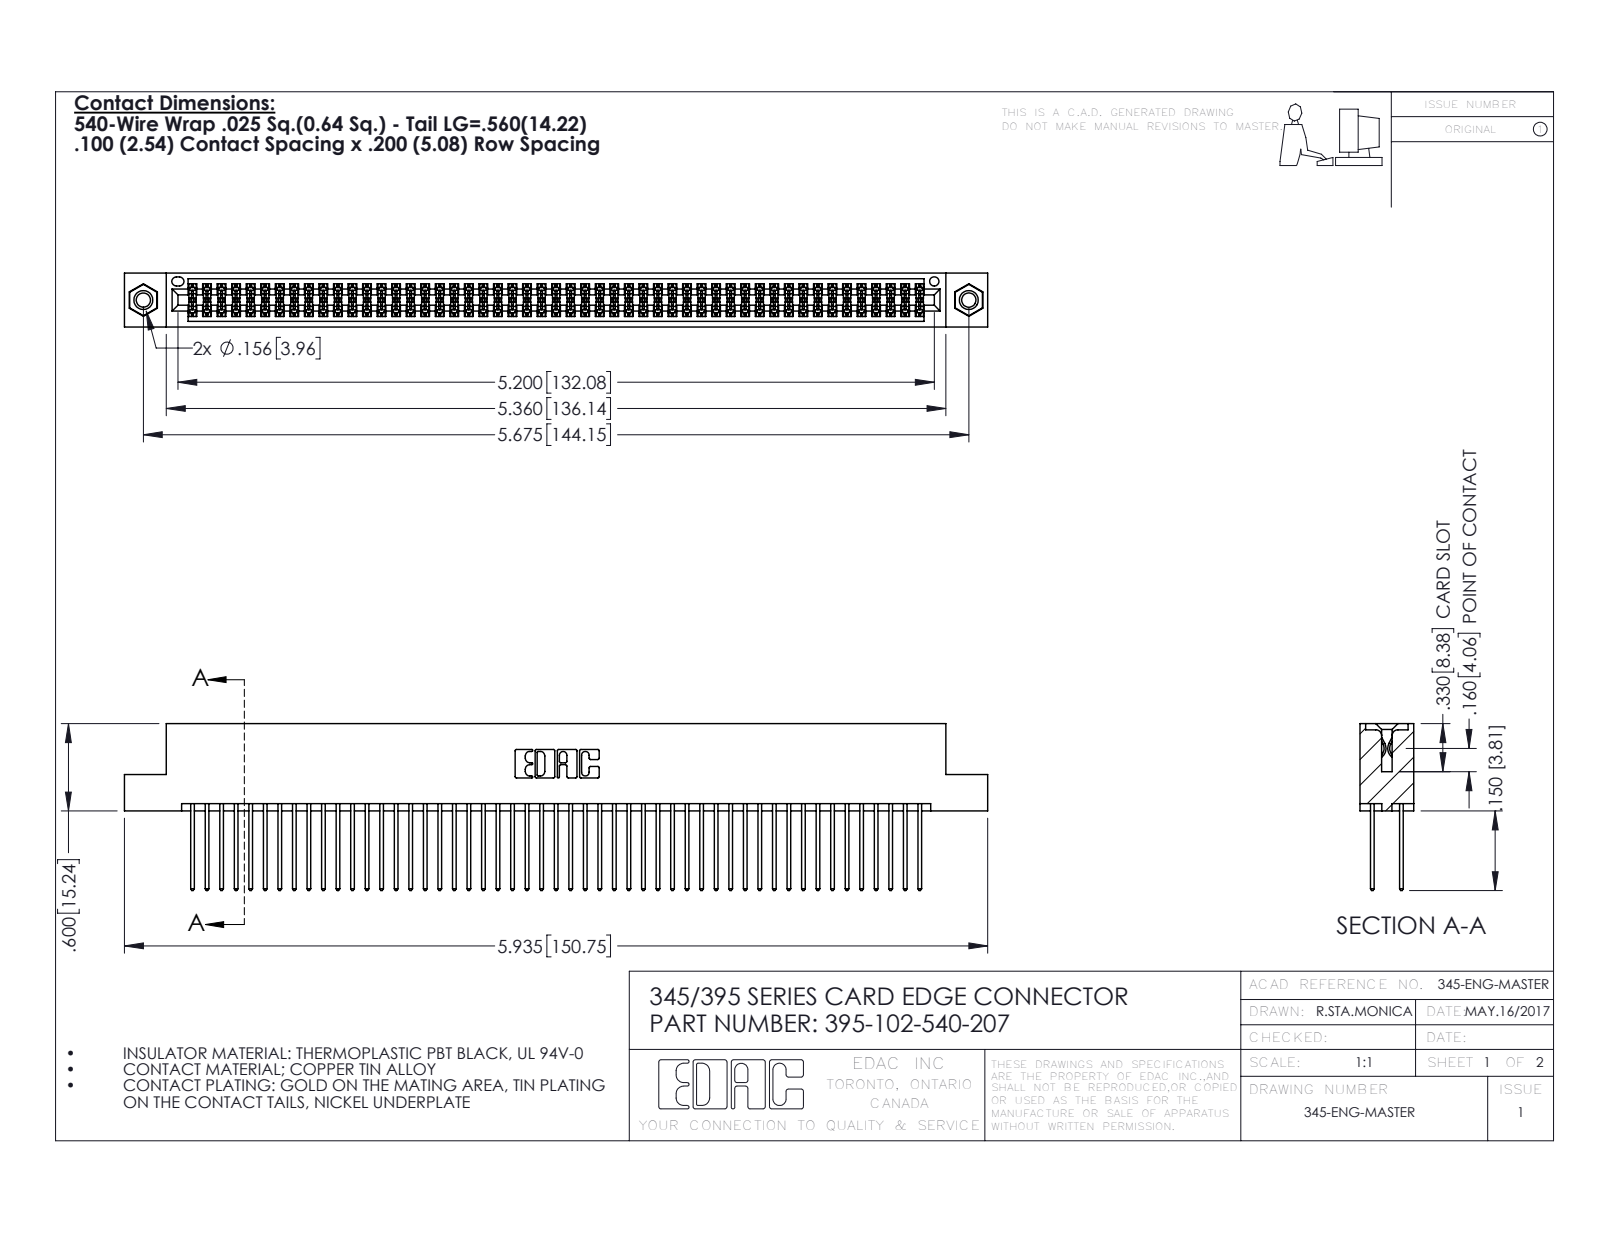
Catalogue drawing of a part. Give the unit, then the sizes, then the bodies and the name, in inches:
Units: inches
Overall size (bounding box): 5.935 × 1.147 × 0.37
Round holes (diameter × count): ⌀0.098 ×2, ⌀0.125 ×2, ⌀0.156 ×2, ⌀0.064 ×1
Round bosses / shafts (diameter × count): ⌀0.155 ×2
Partial cylindrical surfaces — rounded edges, fillets, slot ends (radius × count): R0.006 ×153, R0.01 ×102, R0.01 ×22, R0.007 ×6, R0.031 ×6, R0.026 ×3, R0.014 ×2, R0.019 ×2
Main face-to-face distances: 0.072, 0.298, 0.2, 0.098, 0.272, 0.025, 0.37, 0.225, 0.175, 0.149
Hole centre spacings: 0.27, 5.439, 5.675
Volume: 0.921 in³ · Surface area: 37.69 in²
Bodies: 105 solids, 5286 faces (3478 planar, 1792 cylindrical, 16 other)
Part name (STEP PRODUCT): 395-102-540-207; 345 Part_Flush Mounting Lugs - 0.156 Dia-TI; 345-250-001_345-250-005-103; 345-292-001_345-293-140
STEP written by: SolidWorks 2016 (CONFIG_CONTROL_DESIGN)
